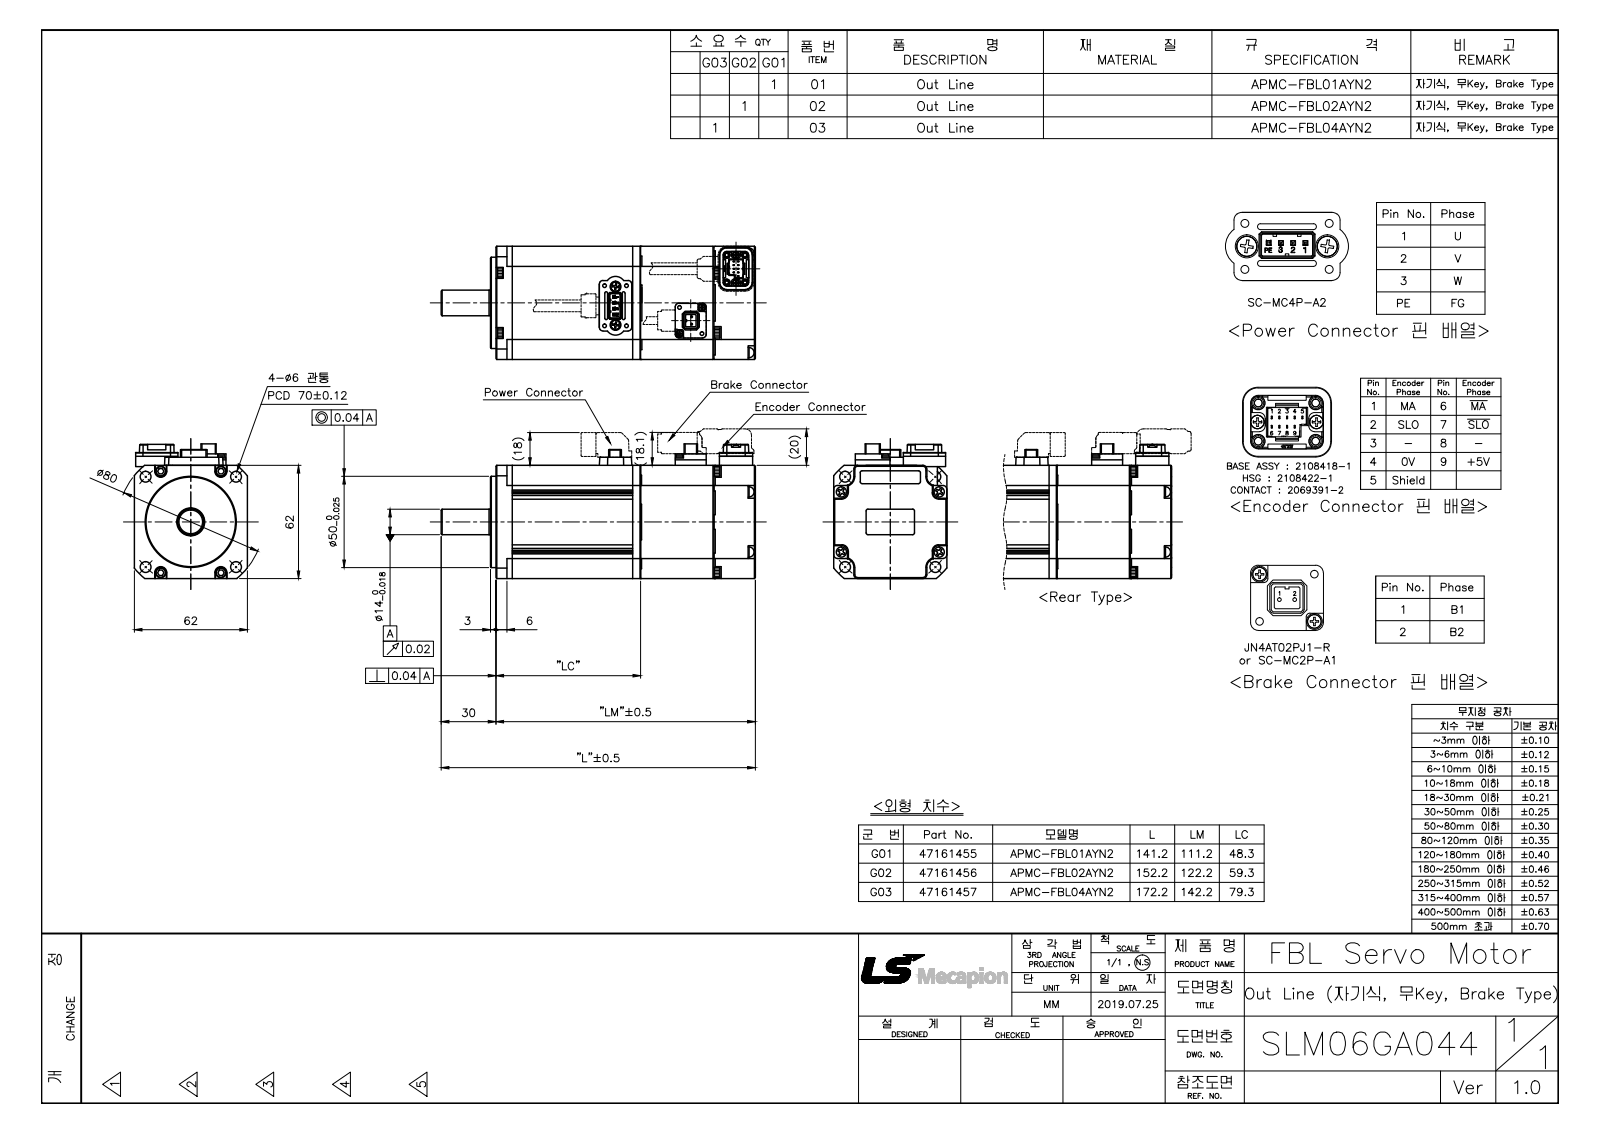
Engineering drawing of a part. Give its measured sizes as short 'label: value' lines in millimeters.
name: SLM06GA044G03_Out Line(APMC-FBL04AYN2)
written by: SolidWorks 2011 (AUTOMOTIVE_DESIGN)
unit: mm
bodies: 50 solids, 2091 faces (1301 planar, 578 cylindrical, 212 other)
size: 172.2 × 73.8 × 62
volume: 494 876 mm³; area: 102 647 mm²
holes: 10× ⌀2.1, 10× ⌀3, 8× ⌀3.5, 6× ⌀1.6, 6× ⌀6, 4× ⌀2, 4× ⌀3.1, 2× ⌀1, 1× ⌀3.3, 1× ⌀3.4, 1× ⌀13, 1× ⌀15.3
bosses: 6× ⌀5.4, 4× ⌀5.6, 4× ⌀5.5, 2× ⌀4.2, 2× ⌀3.6, 2× ⌀3.5, 2× ⌀2.2, 2× ⌀0.9
rounds: 20× R0.2, 20× R0.3, 12× R1, 12× R2, 12× R3, 9× R0.15, 7× R0.45, 6× R0.11
face distances: 62, 0.7, 4.3, 0.5, 66, 70.3, 44.5, 40.2, 110.5, 40.9
hole spacings: 5, 6.02, 8.5, 8.8, 9.43, 15.29, 16, 22.32
